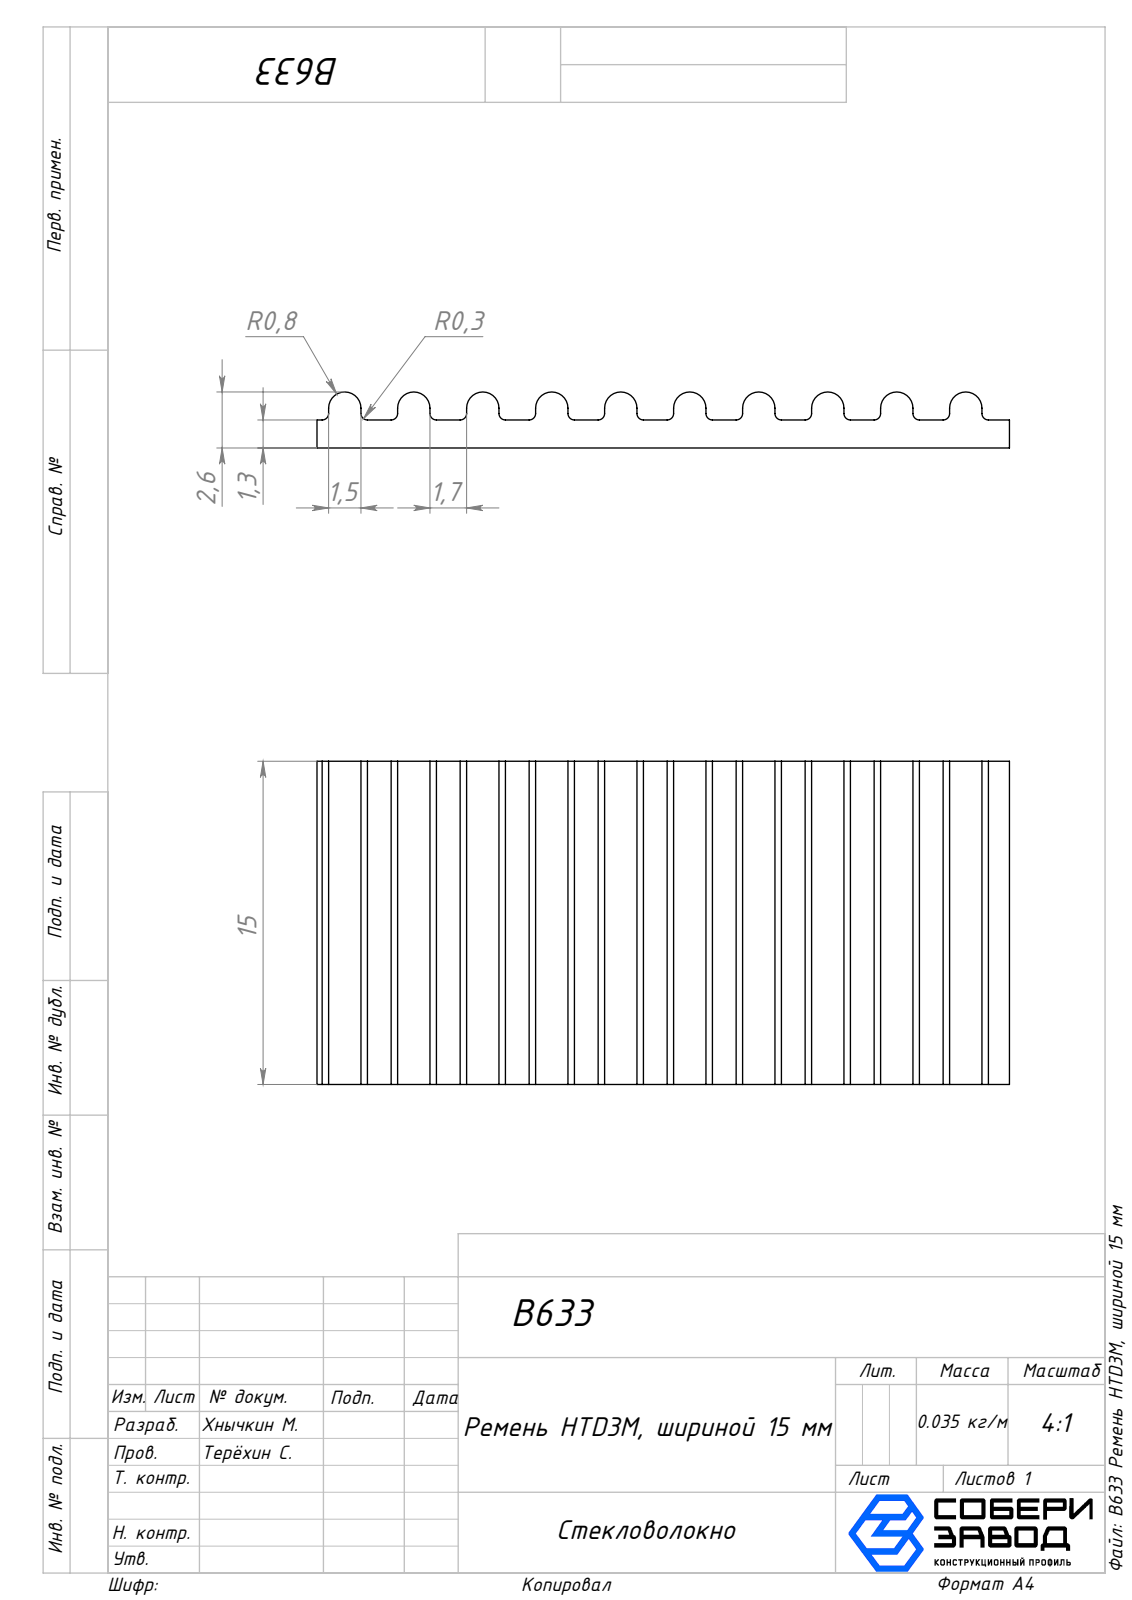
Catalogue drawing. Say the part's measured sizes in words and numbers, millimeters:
The part is named "B633 Ремень HTD3M, шириной 15 мм". Its 3-D file was written by "SolidWorks 2025 (AUTOMOTIVE_DESIGN)". It is 1 solid with 66 faces: 36 planar, 30 cylindrical and 0 other. Overall it measures 32.12 by 15 by 2.6 millimeters. Its volume is 888 cubic millimeters and its surface area 1 376 square millimeters. Partial cylindrical surfaces (rounded edges, fillets, slot ends): 20 of radius 0.3, 10 of radius 0.75. The main face-to-face distances are 1.3, 15, 3.2, 6.4, 9.6, 12.8, 1.5, 16, 4.7, 1.7.
